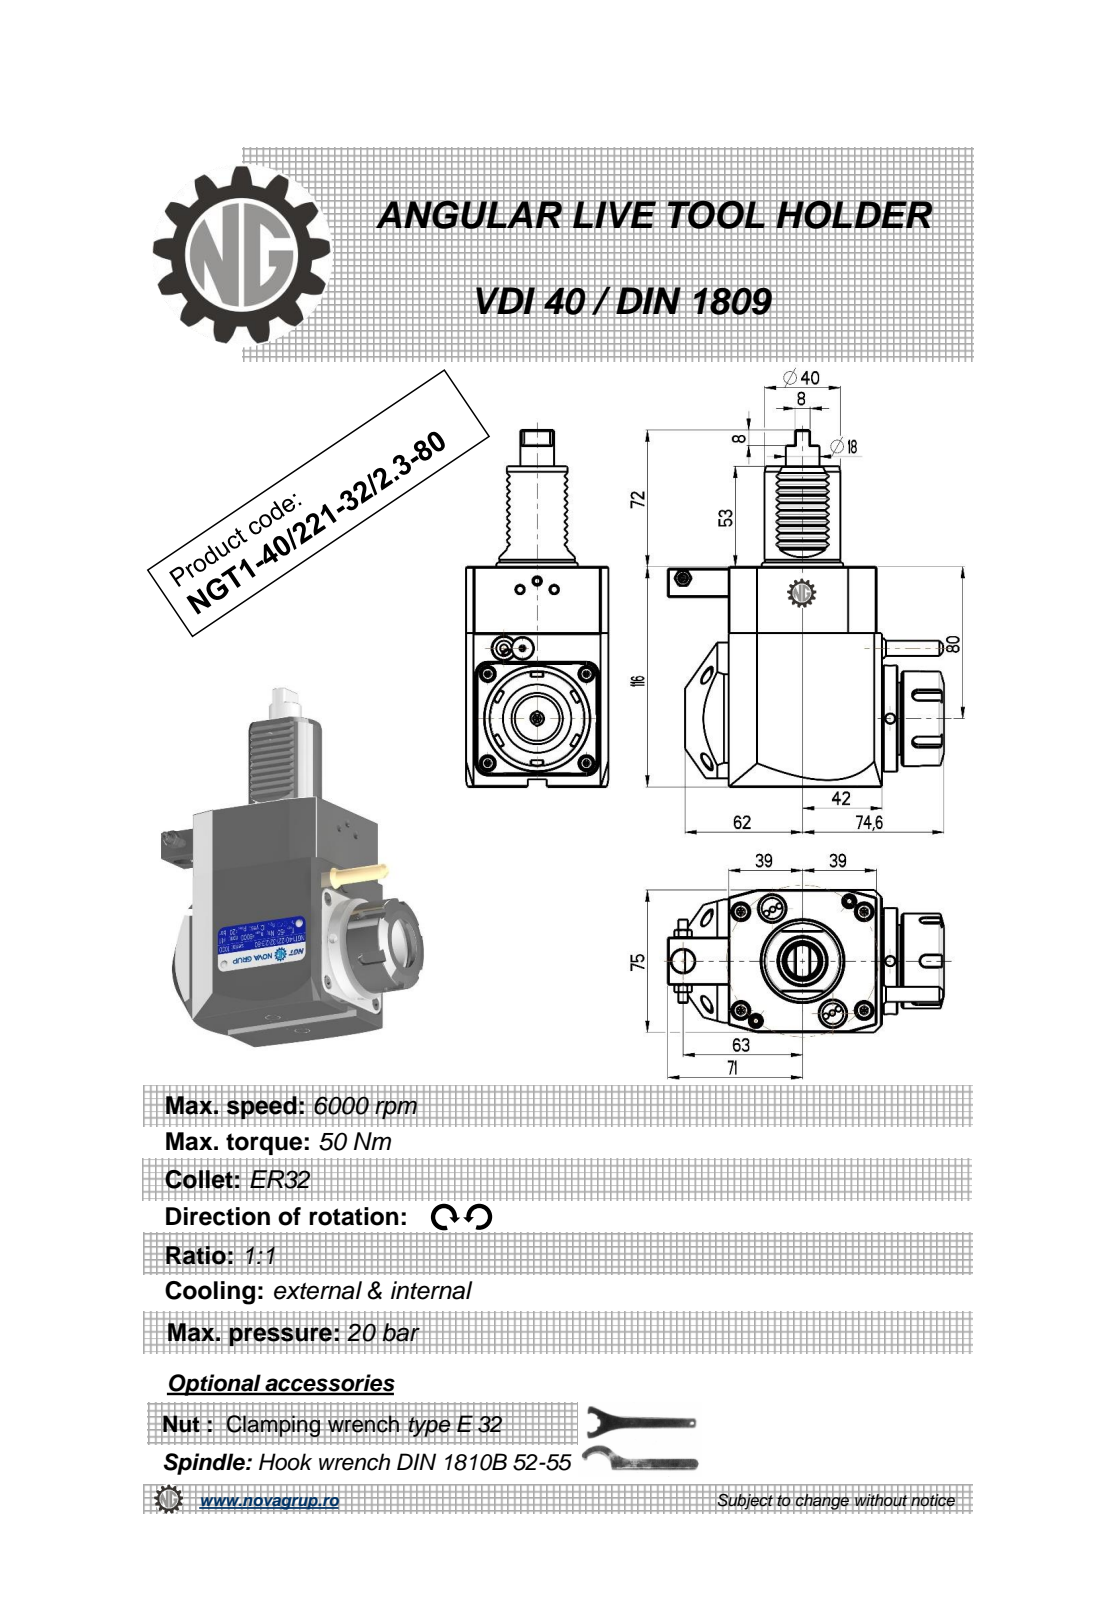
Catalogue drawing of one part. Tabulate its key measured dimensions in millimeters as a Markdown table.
| quantity | value |
| --- | --- |
| part name | NGT1_40_221_32_2_3_80 |
| STEP written by | PRO/ENGINEER BY PARAMETRIC TECHNOLOGY CORPORATION, 2010280 (CONFIG_CONTROL_DESIGN) |
| units | millimeters |
| bodies | 1 solid, 459 faces (228 planar, 94 cylindrical, 137 other) |
| overall size | 188 × 145.6 × 75 |
| volume | 883 412 mm³ |
| surface area | 71 582 mm² |
| round holes (diameter × count) | 5 × 3, 3 × 1, 4.2 × 1, 9.5 × 1, 12 × 1, 27 × 1 |
| round bosses / shafts (diameter × count) | 56 × 1, 50 × 1, 43 × 1, 40 × 1, 17.8 × 1, 11.2 × 1, 8.96 × 1, 8 × 1 |
| partial cylindrical surfaces (radius × count) | 0.3 × 20, 0.26 × 12, 0.22 × 6, 3 × 5, 0.8 × 2, 40 × 1 |
| main face-to-face distances | 75, 116, 81, 78, 3, 80.8, 2.8, 112, 7.5, 11 |
| hole center spacings | 39.58, 40.93, 72.5, 109.25, 131.95 |
